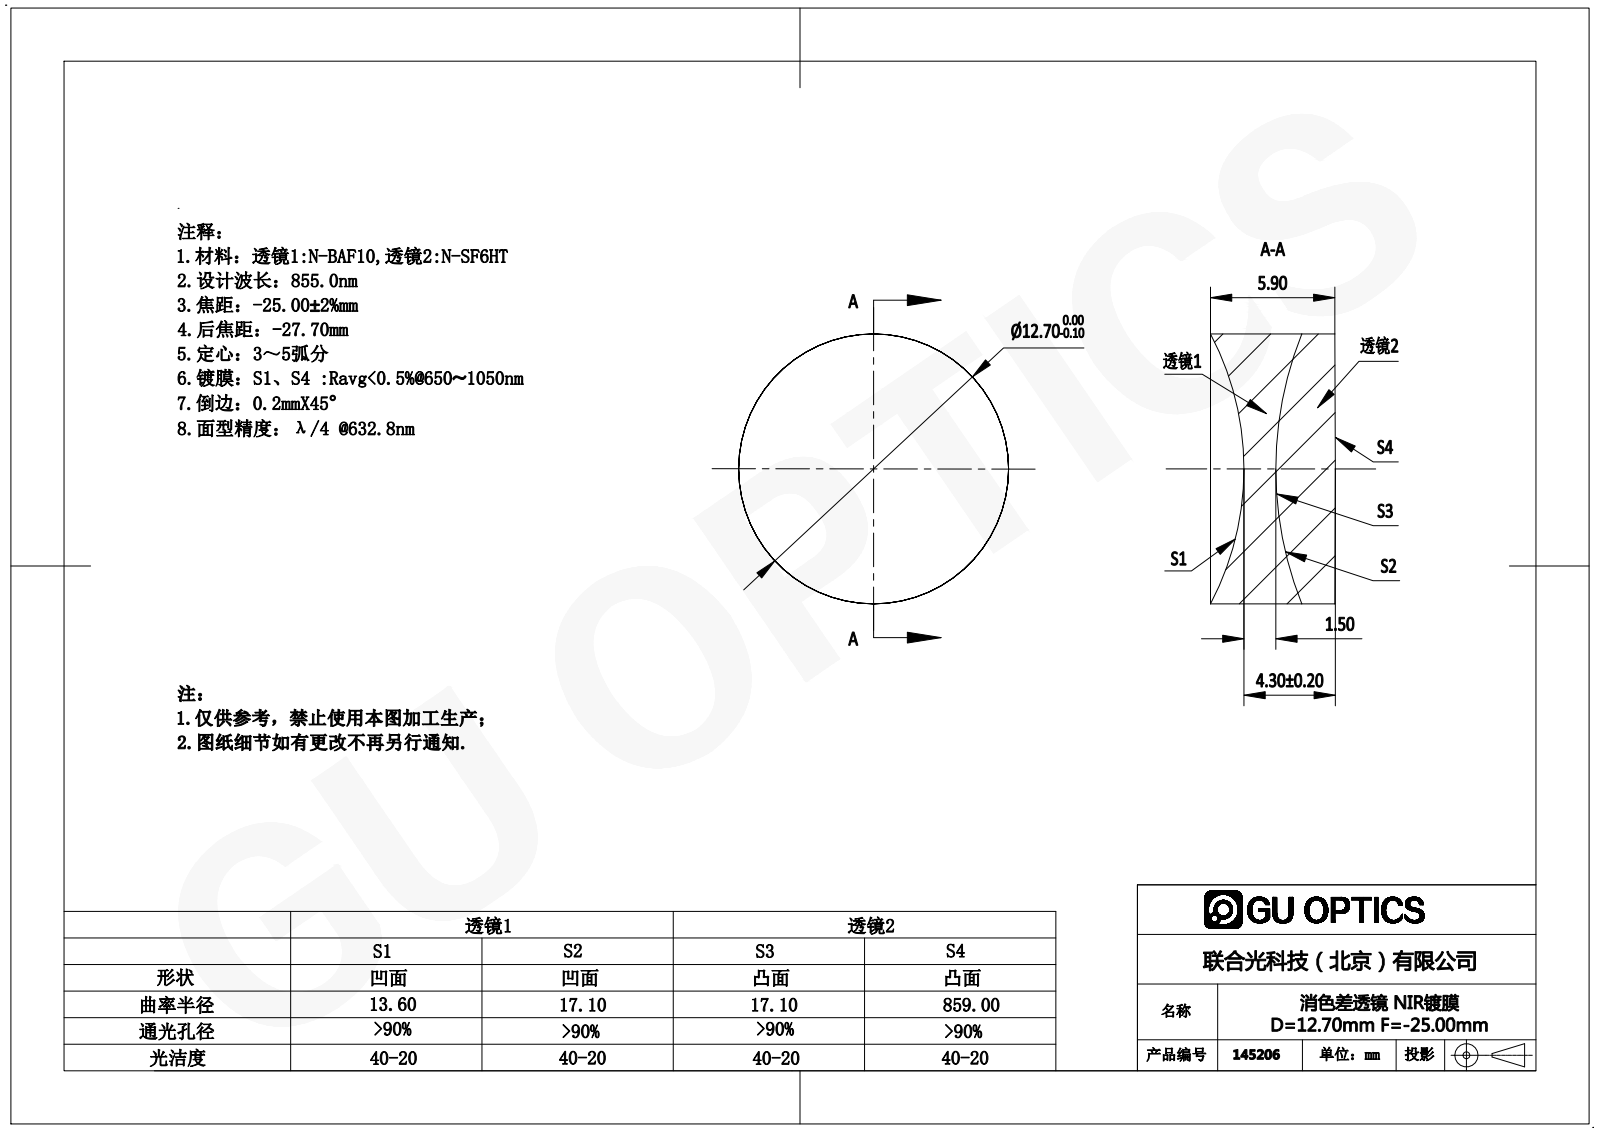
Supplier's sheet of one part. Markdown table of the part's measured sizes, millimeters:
| quantity | value |
| --- | --- |
| part name | 145206 |
| STEP written by | SolidWorks 2016 (AUTOMOTIVE_DESIGN) |
| units | millimeters |
| bodies | 2 solids, 12 faces (0 planar, 4 cylindrical, 8 other) |
| overall size | 12.7 × 12.7 × 5.87 |
| volume | 641 mm³ |
| surface area | 757 mm² |
| round bosses / shafts (diameter × count) | 12.7 × 1 |
